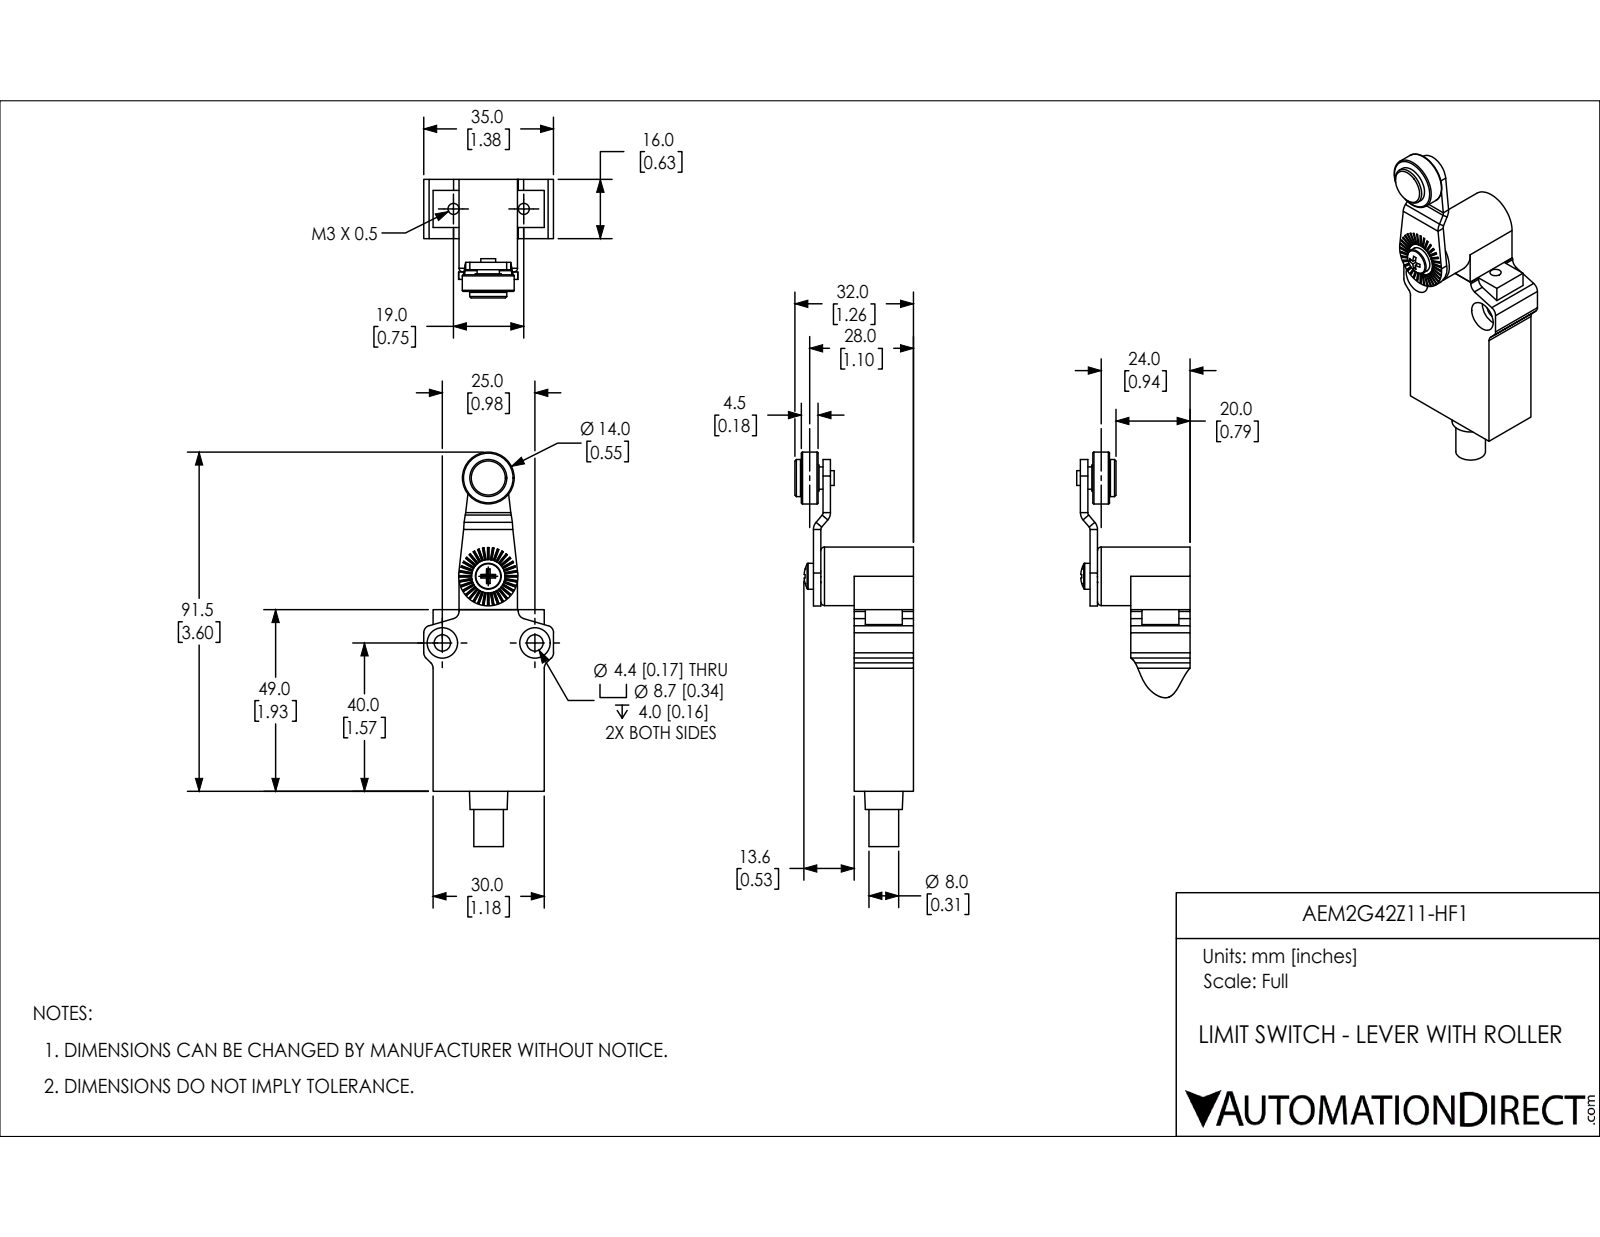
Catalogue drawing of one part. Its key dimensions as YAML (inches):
part_name: "AEM2G42Z11-HF1"
step_written_by: "SolidWorks 2018 (AUTOMOTIVE_DESIGN)"
units: inches
bodies: {solids: 6, faces: 590, planar: 297, cylindrical: 121, other: 172}
overall_size: [4.189, 1.378, 1.26]
volume: 1.872
surface_area: 17.57
round_holes:
  - {diameter: 0.118, count: 2}
  - {diameter: 0.173, count: 2}
  - {diameter: 0.323, count: 2}
  - {diameter: 0.098, count: 1}
  - {diameter: 0.161, count: 1}
  - {diameter: 0.197, count: 1}
  - {diameter: 0.224, count: 1}
round_bosses_or_shafts:
  - {diameter: 0.276, count: 2}
  - {diameter: 0.622, count: 1}
  - {diameter: 0.551, count: 1}
  - {diameter: 0.394, count: 1}
  - {diameter: 0.315, count: 1}
  - {diameter: 0.236, count: 1}
  - {diameter: 0.197, count: 1}
  - {diameter: 0.157, count: 1}
partial_cylinders:
  - {radius: 0.079, count: 8}
  - {radius: 0.039, count: 2}
  - {radius: 0.118, count: 2}
  - {radius: 0.256, count: 1}
  - {radius: 0.315, count: 1}
face_to_face_distances: [0.63, 1.181, 0.354, 1.929, 0.079, 0.984, 0.102, 0.472, 0.906, 0.276]
hole_center_spacings: [0.748, 0.861, 0.865, 0.984, 1.043, 1.819, 1.821]
